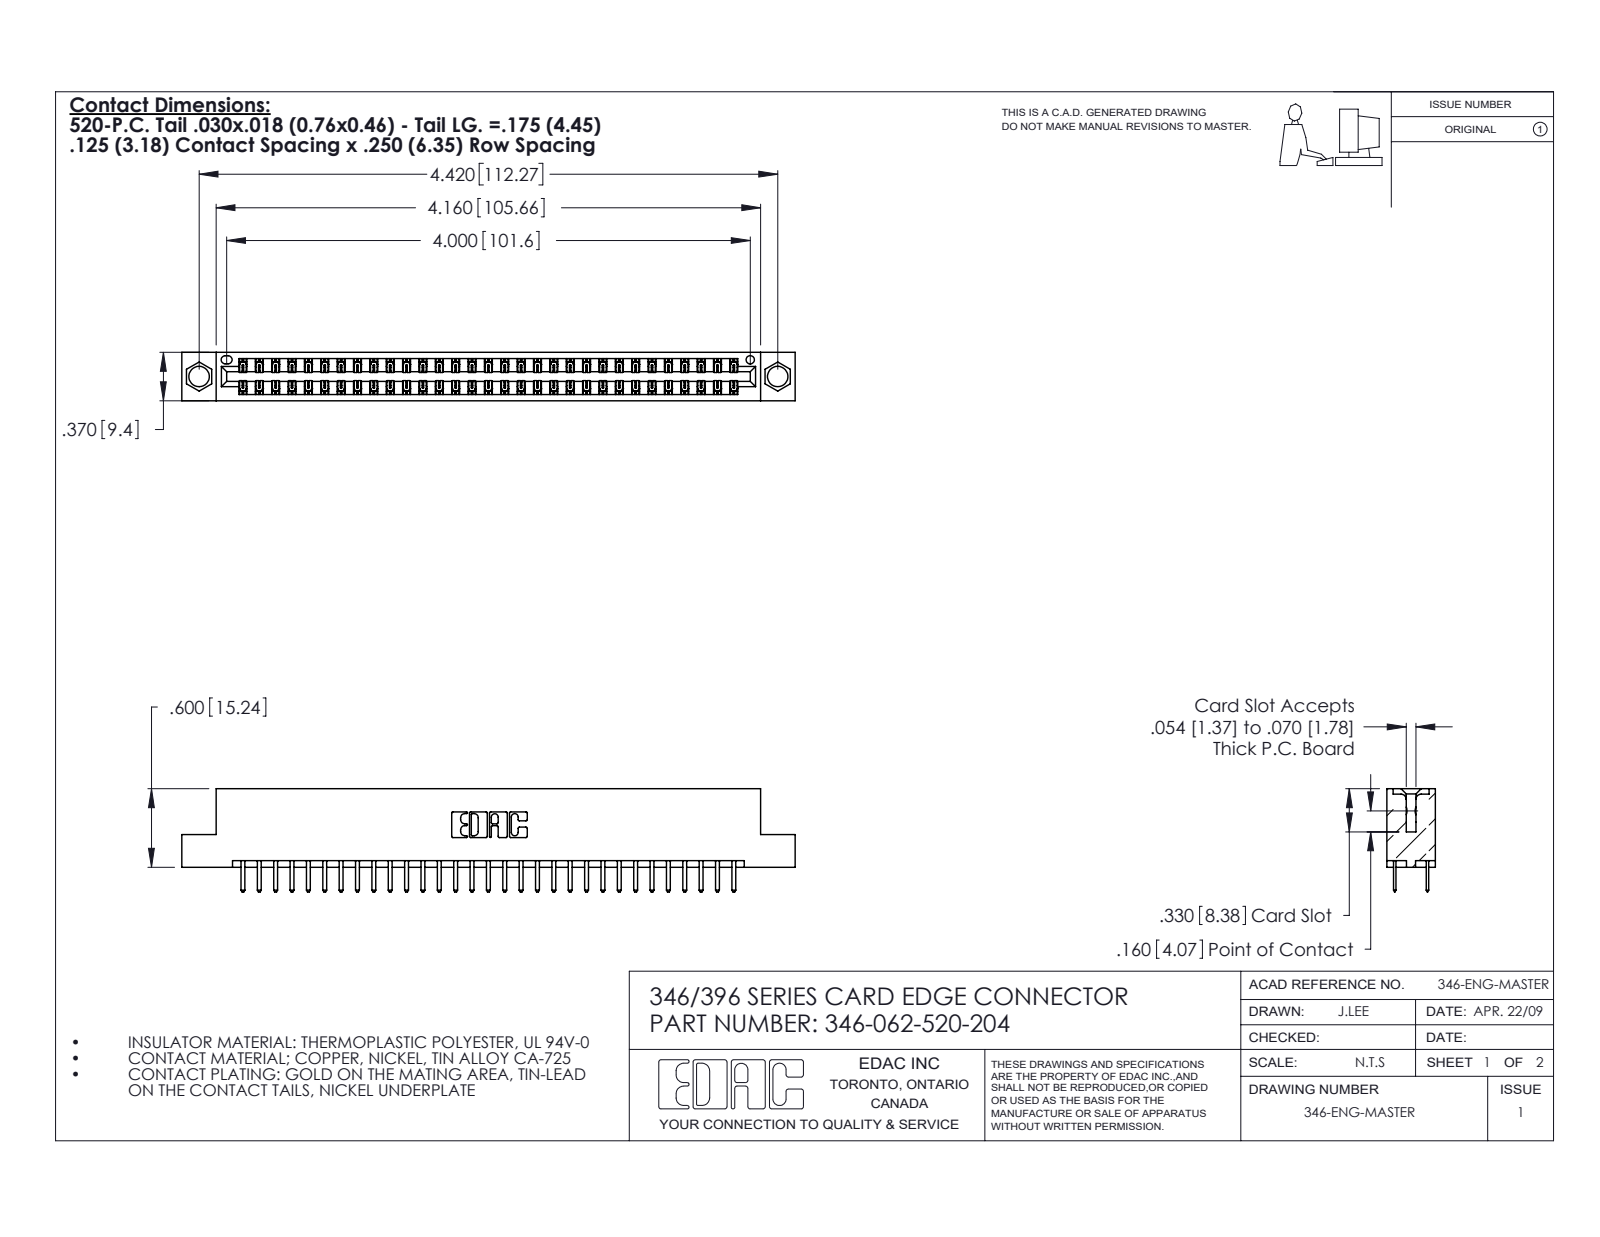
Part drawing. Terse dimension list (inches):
name: 346 Part_Flush Mounting Lugs - 0.156 Dia-TH; 346-062-520-204; 345-292-001_345-293-120
written by: SolidWorks 2020 (CONFIG_CONTROL_DESIGN)
unit: in
bodies: 63 solids, 3608 faces (2384 planar, 1224 cylindrical, 0 other)
size: 4.685 × 0.788 × 0.37
volume: 0.695 in³; area: 23.65 in²
holes: 2× ⌀0.156, 1× ⌀0.064
rounds: 93× R0.006, 66× R0.01, 22× R0.01, 6× R0.007, 6× R0.031, 3× R0.026, 2× R0.014, 2× R0.022
face distances: 0.048, 0.322, 0.25, 0.37, 0.275, 0.072, 0.298, 0.025, 0.148, 0.222
hole spacings: 0.246, 4.212, 4.42
